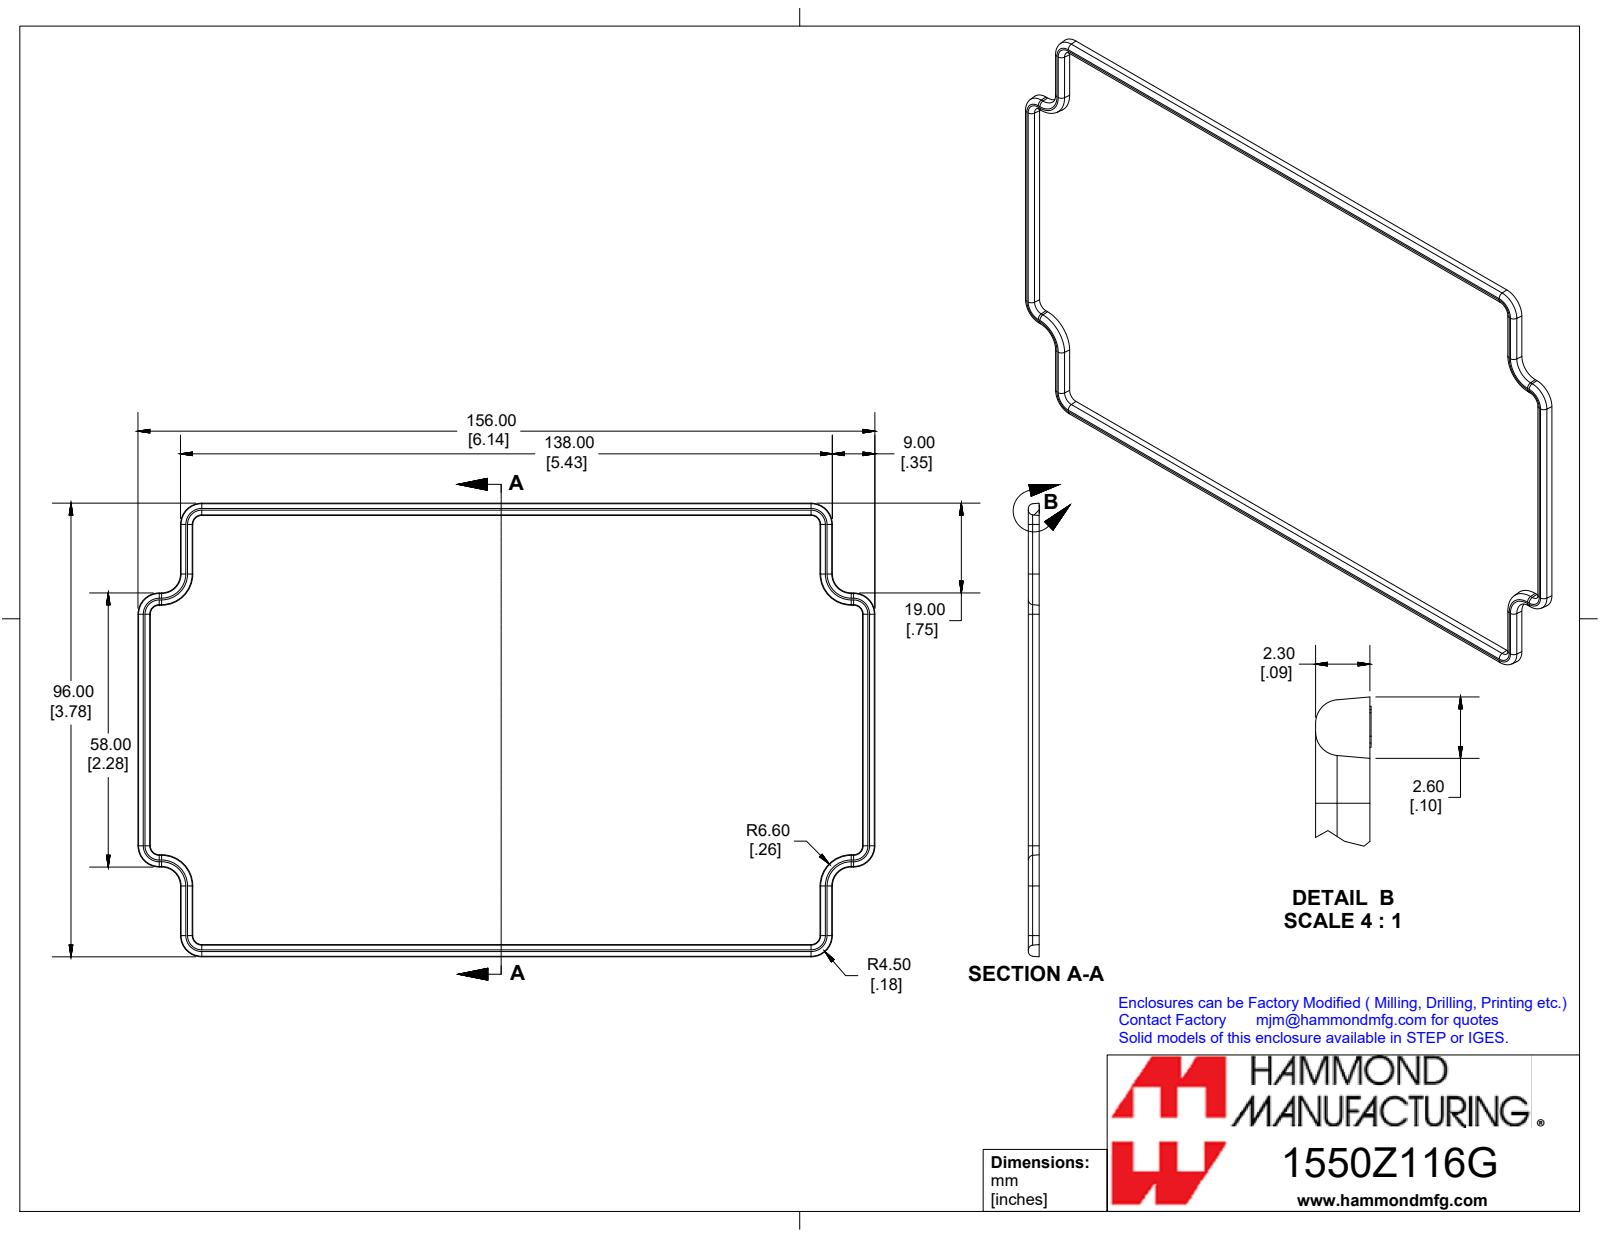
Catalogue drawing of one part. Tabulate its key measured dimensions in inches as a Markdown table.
| quantity | value |
| --- | --- |
| part name | 1550Z116GASKET |
| STEP written by | SolidWorks 2019 (CONFIG_CONTROL_DESIGN) |
| units | inches |
| bodies | 1 solid, 150 faces (41 planar, 24 cylindrical, 85 other) |
| overall size | 6.142 × 3.78 × 0.093 |
| volume | 0.149 in³ |
| surface area | 6.4 in² |
| partial cylindrical surfaces (radius × count) | 0.039 × 16 |
| main face-to-face distances | 3.663, 0.091, 6.015, 0.353, 5.662, 5.309, 0.745, 2.917, 0.093, 2.172 |
